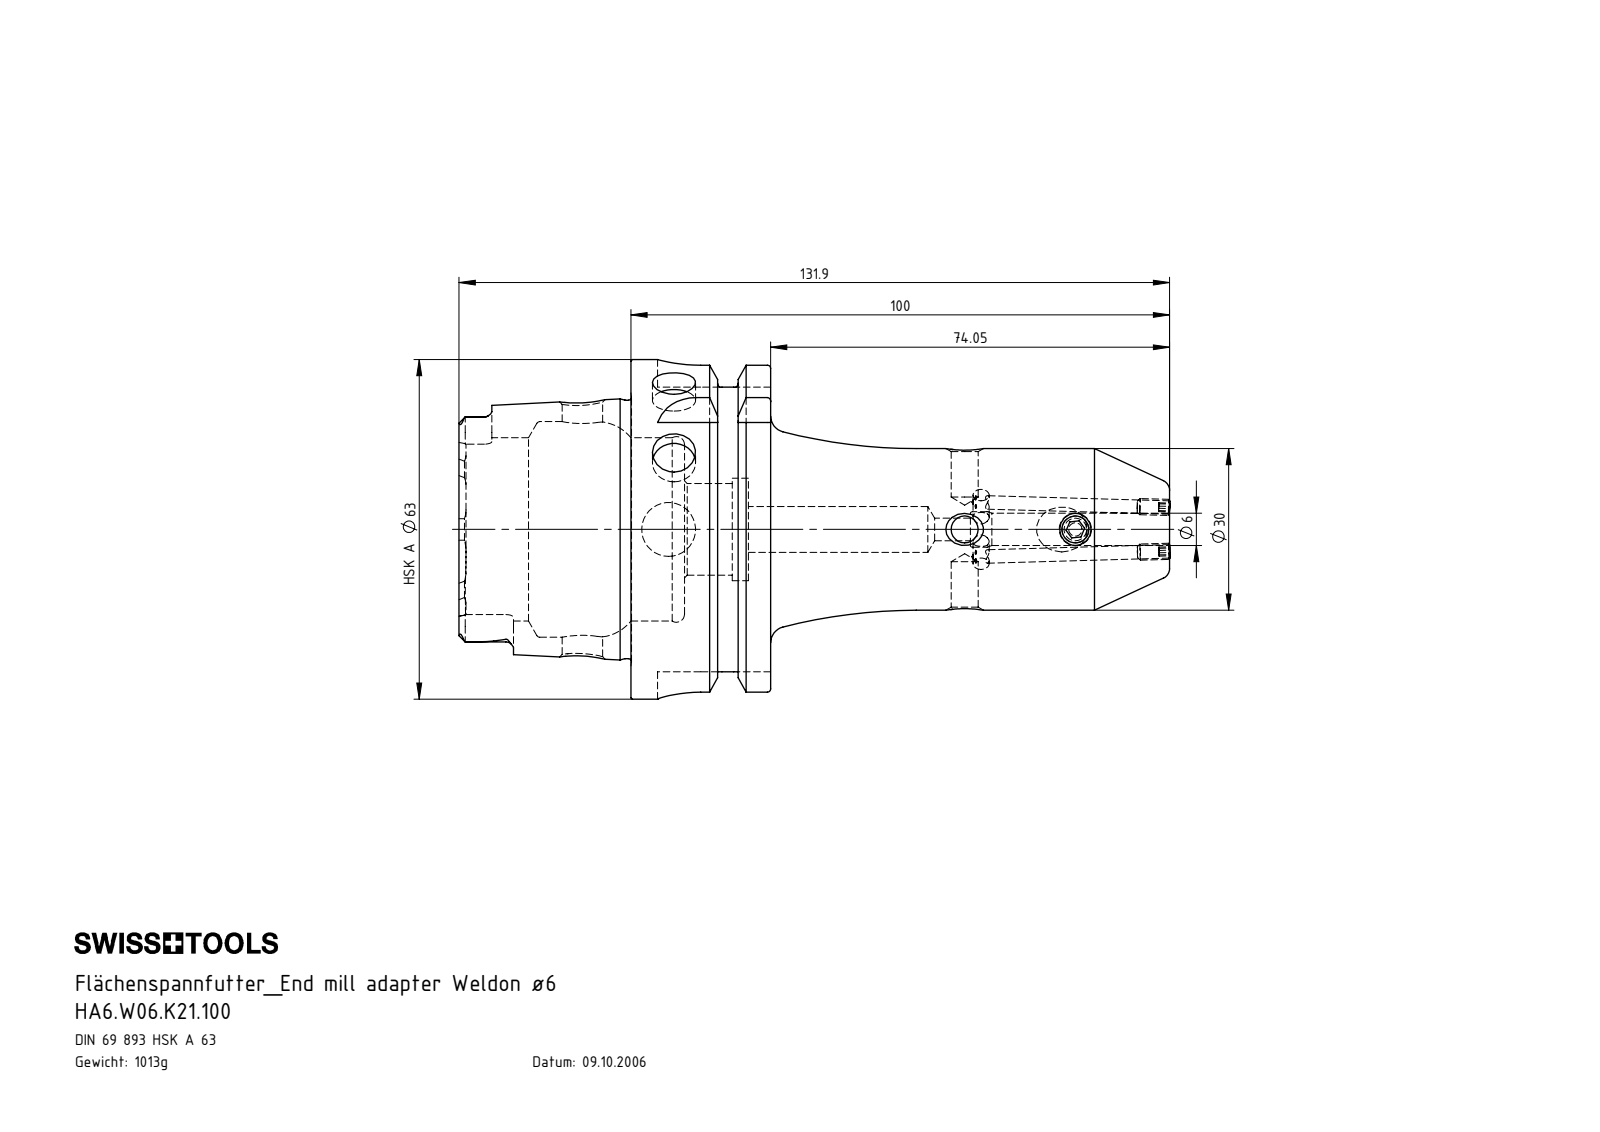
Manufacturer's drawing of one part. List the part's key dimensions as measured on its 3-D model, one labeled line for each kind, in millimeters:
Part name (STEP PRODUCT): HA6-W06.K21.100; ERU-CJ2.001.006; W06-ER1.001.010; HA6-W06.K21.100_C_Fertigbearbeitung
STEP written by: SolidWorks 2012 (AUTOMOTIVE_DESIGN)
Units: millimetres
Bodies: 4 solids, 292 faces (77 planar, 83 cylindrical, 132 other)
Overall size (bounding box): 131.98 × 63 × 63
Volume: 128 978 mm³ · Surface area: 31 916 mm²
Round holes (diameter × count): ⌀5 ×3, ⌀2.5 ×2, ⌀8 ×2, ⌀3 ×1, ⌀4.2 ×1, ⌀6 ×1, ⌀6.6 ×1, ⌀7.5 ×1, ⌀8.5 ×1, ⌀10 ×1, ⌀17 ×1, ⌀19 ×1
Round bosses / shafts (diameter × count): ⌀3 ×2, ⌀63 ×1, ⌀54.95 ×1, ⌀47.94 ×1, ⌀30 ×1, ⌀6 ×1
Partial cylindrical surfaces — rounded edges, fillets, slot ends (radius × count): R1.4 ×6, R2.88 ×4, R8 ×4
Main face-to-face distances: 25.95, 16, 9.95, 31.9, 41.85, 57.85, 52.8, 21.8, 11.85, 53.7
Hole centre spacings: 20.55, 54.95, 70.95, 75.5
